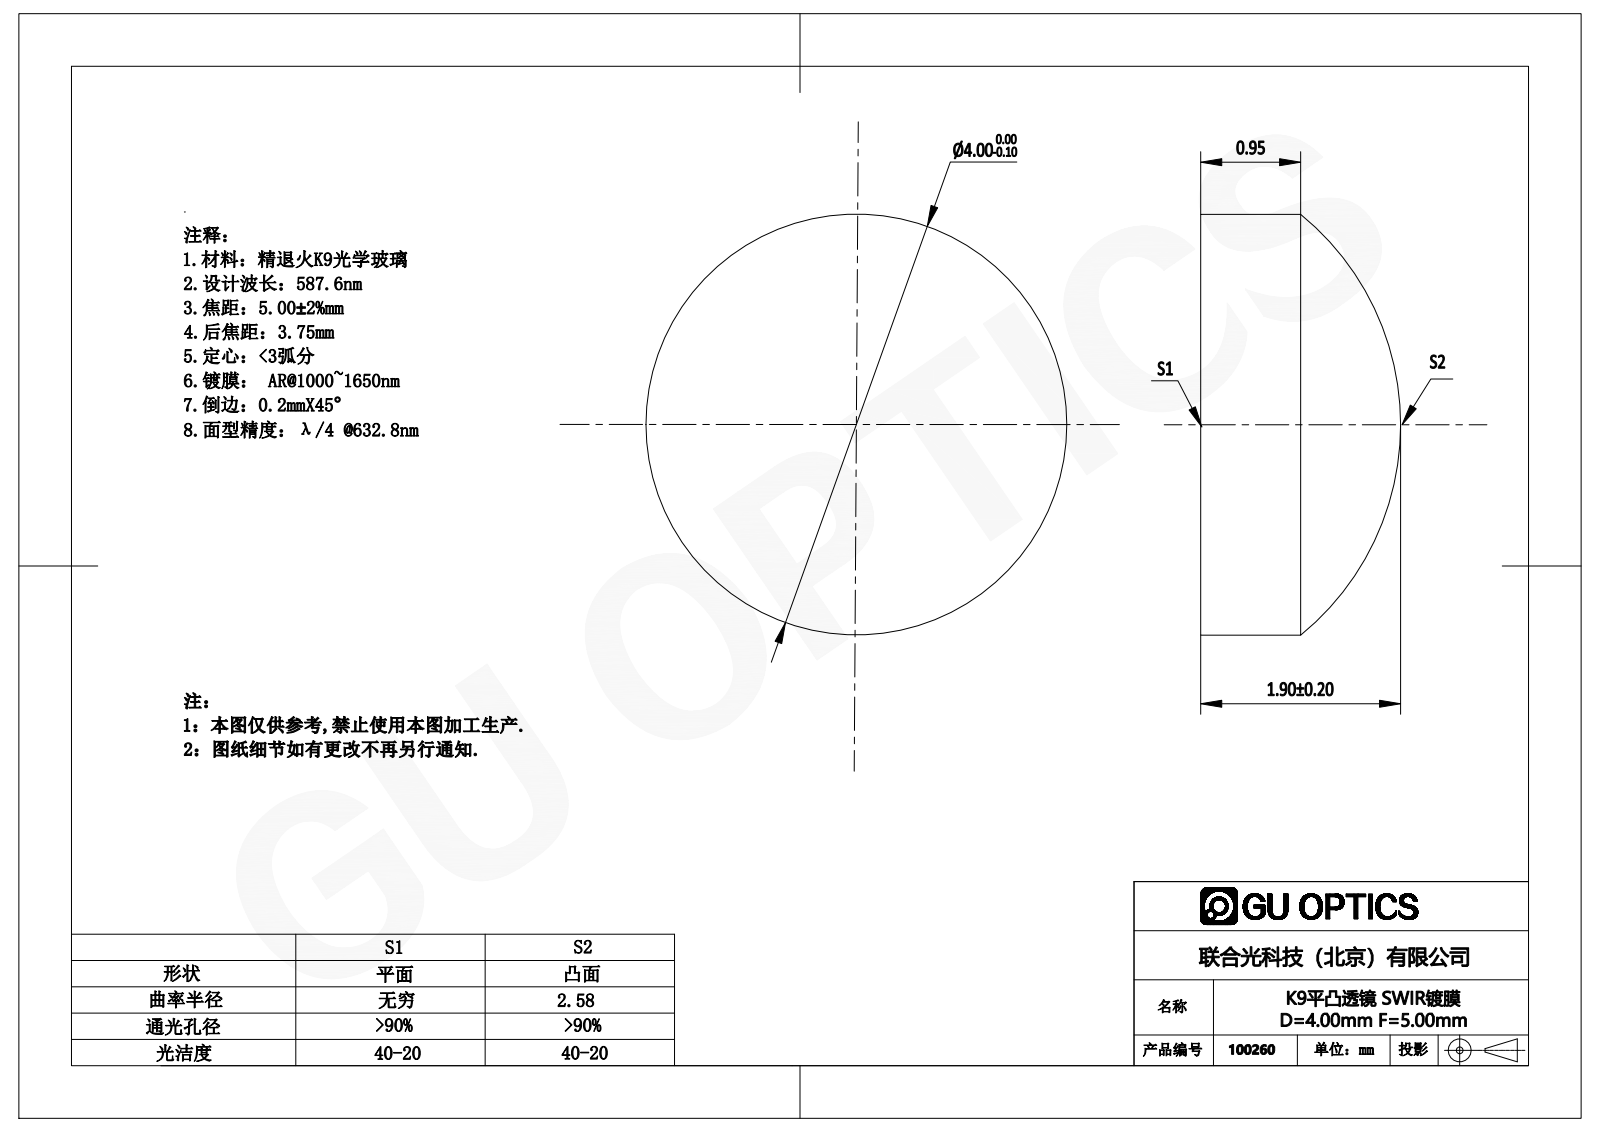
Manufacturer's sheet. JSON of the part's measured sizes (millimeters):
{"part_name": "100088", "step_written_by": "SolidWorks 2016 (AUTOMOTIVE_DESIGN)", "units": "millimeters", "bodies": {"solids": 1, "faces": 5, "planar": 1, "cylindrical": 2, "other": 2}, "overall_size": [4, 4, 1.9], "volume_mm3": 18, "surface_area_mm2": 40, "round_bosses_or_shafts": [[4, 1]]}
